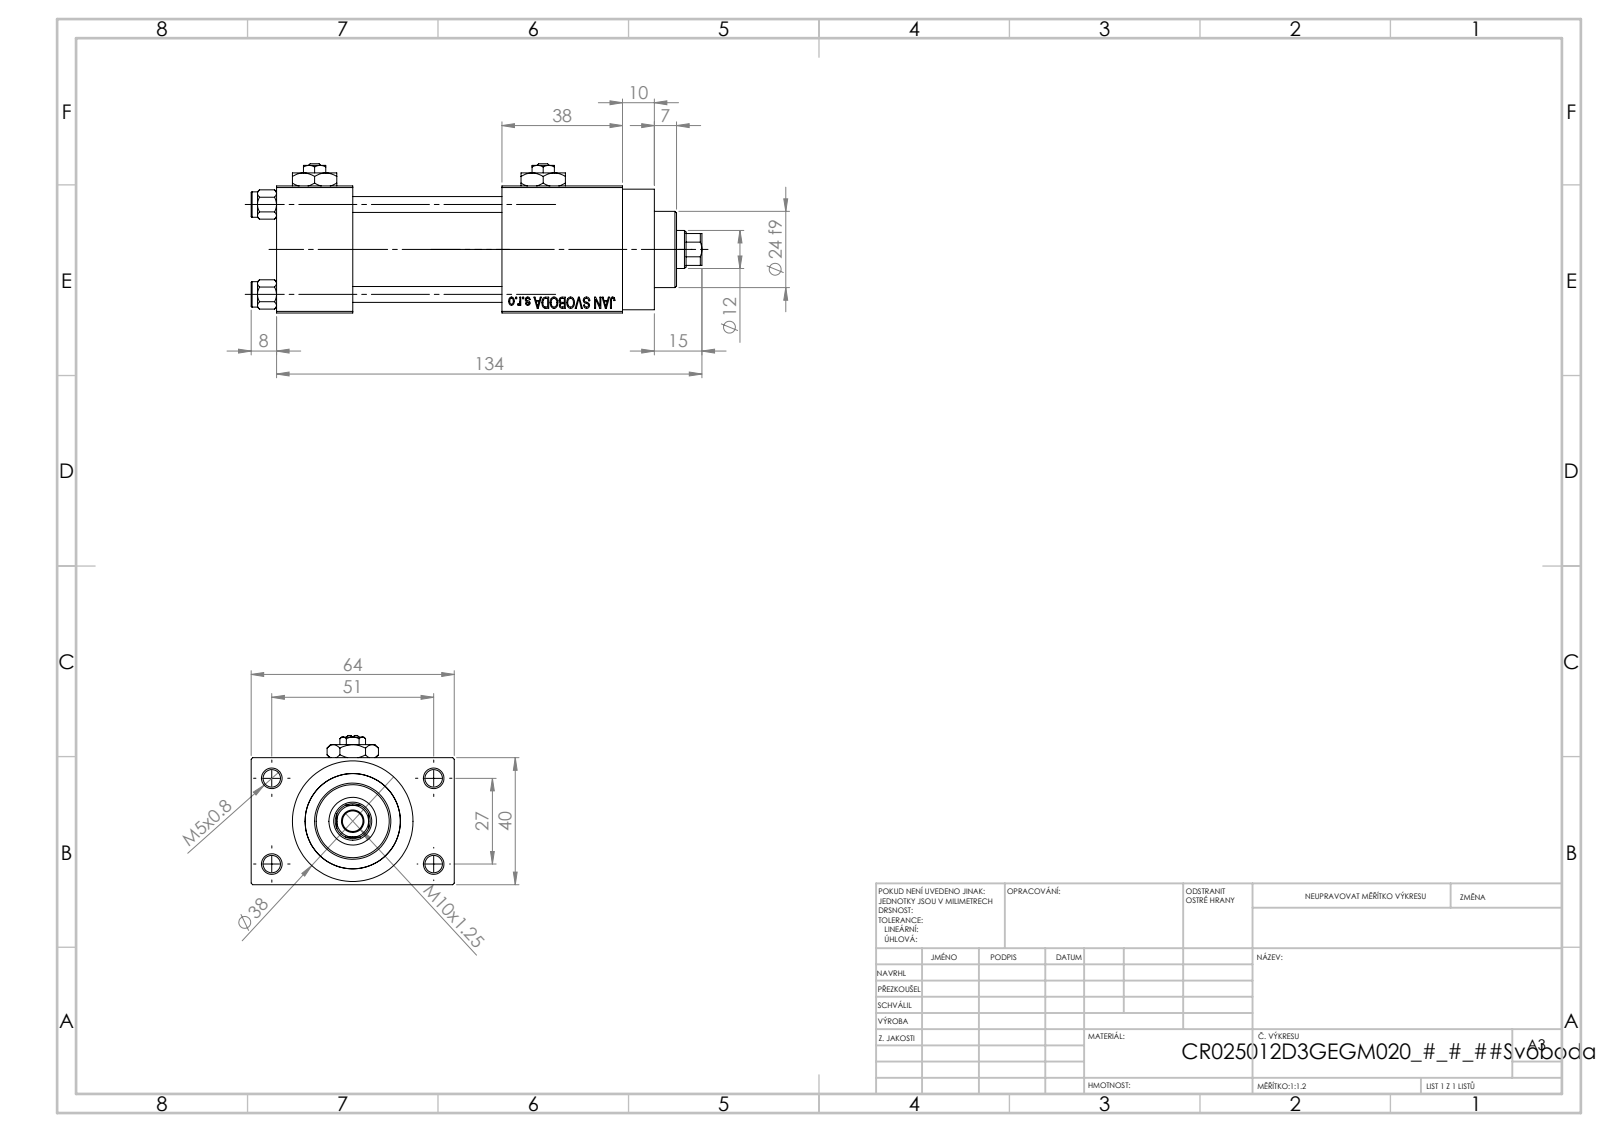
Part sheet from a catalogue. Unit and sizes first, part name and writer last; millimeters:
Units: millimetres
Overall size (bounding box): 142 × 64 × 47
Round holes (diameter × count): ⌀5 ×4, ⌀5.5 ×4, ⌀20 ×3, ⌀7 ×2, ⌀13.16 ×2, ⌀6.5 ×1, ⌀12 ×1, ⌀15 ×1, ⌀25 ×1, ⌀30 ×1
Round bosses / shafts (diameter × count): ⌀8 ×4, ⌀38 ×1, ⌀31 ×1, ⌀24 ×1
Partial cylindrical surfaces — rounded edges, fillets, slot ends (radius × count): R5.5 ×1
Main face-to-face distances: 40, 52, 12, 47, 24, 71, 64, 38, 85, 109
Hole centre spacings: 11.37, 20.01, 28.3, 28.85, 29.89, 39.66, 48.34, 27
Volume: 174 214 mm³ · Surface area: 63 315 mm²
Bodies: 13 solids, 1202 faces (542 planar, 100 cylindrical, 560 other)
Part name (STEP PRODUCT): NUT_M5_D; V215_VC_A; V215CR_D_Body; Zatka_pro_OIL_PORT (+2 more)
STEP written by: SolidWorks 2019 (CONFIG_CONTROL_DESIGN)
